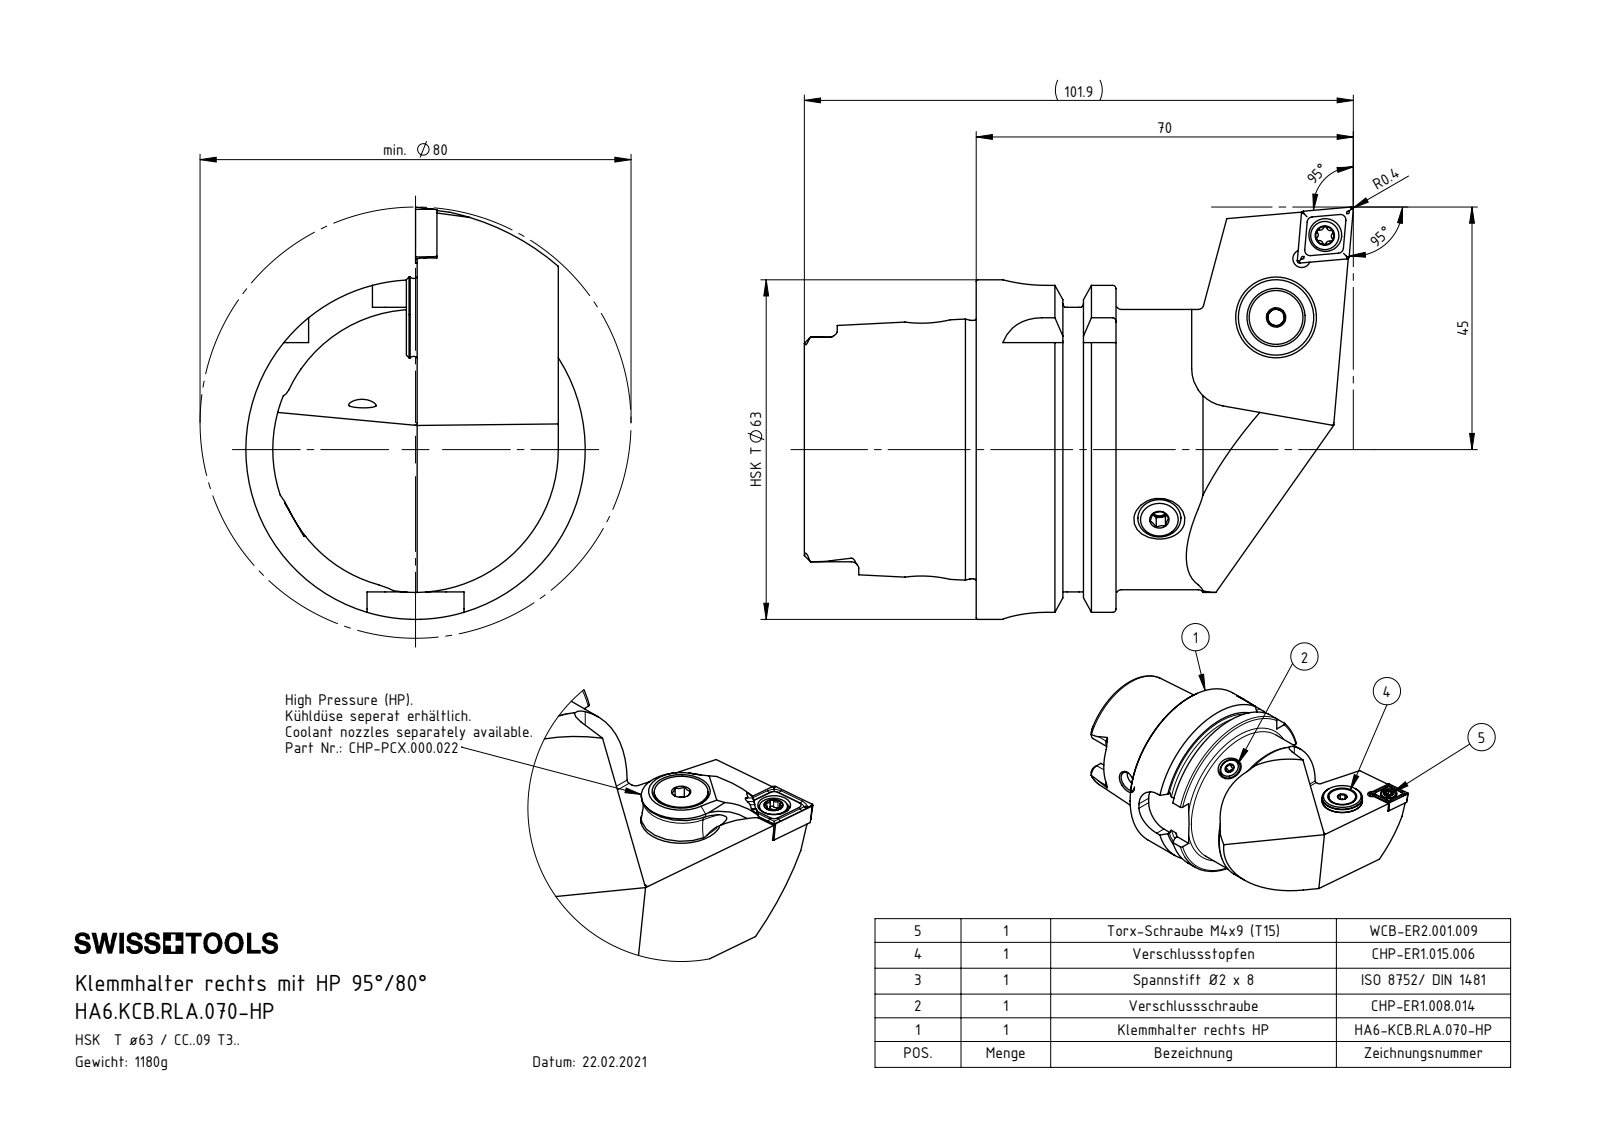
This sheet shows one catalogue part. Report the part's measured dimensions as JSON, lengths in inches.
{"part_name": "ISO 8752 2x8; CCMT09T304; CHP-ER1.015.006_A; CHP-ER1.008.014_A (+6 more)", "step_written_by": "SolidWorks 2017 (AUTOMOTIVE_DESIGN)", "units": "inches", "bodies": {"solids": 8, "faces": 307, "planar": 117, "cylindrical": 75, "other": 115}, "overall_size": [4.012, 3.012, 2.48], "volume_in3": 9.197, "surface_area_in2": 52.01, "round_holes": [[0.13, 2], [0.165, 2], [0.197, 2], [0.047, 1], [0.079, 1], [0.098, 1], [0.118, 1], [0.173, 1], [0.205, 1], [0.24, 1], [0.276, 1], [0.295, 1]], "round_bosses_or_shafts": [[2.48, 1], [2.163, 1], [2.047, 1], [1.887, 1], [0.591, 1], [0.528, 1], [0.394, 1], [0.315, 1]], "partial_cylinders_radius": [[0.013, 6], [0.023, 6], [0.055, 6], [0.315, 4], [0.02, 2], [0.111, 2], [0.113, 2], [0.276, 1]], "face_to_face_distances": [1.031, 1.022, 0.63, 0.392, 1.256, 1.648, 2.278, 2.079, 0.858, 0.467], "hole_center_spacings": [0.177, 0.239, 0.244, 0.322, 0.468, 0.56, 0.565, 0.696]}
